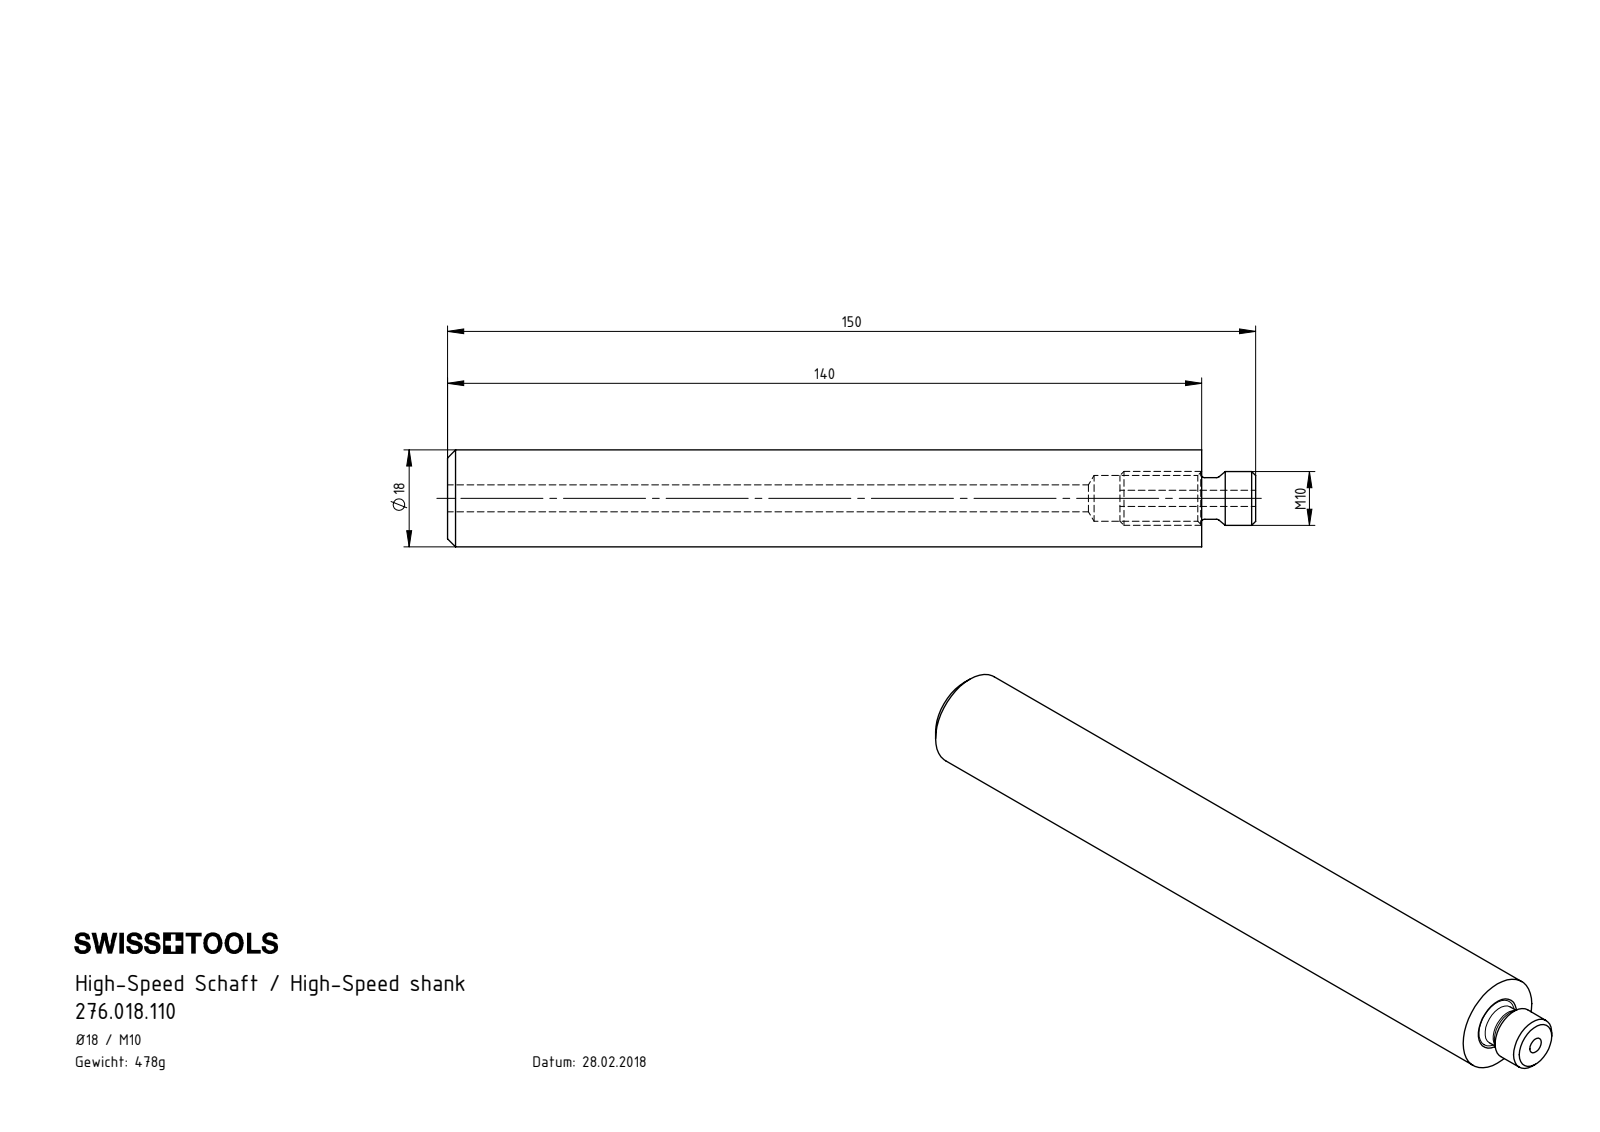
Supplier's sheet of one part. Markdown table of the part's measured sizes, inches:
| quantity | value |
| --- | --- |
| part name | 276.018.110; HM1-U18.001.140_A; HM1-BG1.010.025_A |
| STEP written by | SolidWorks 2017 (CONFIG_CONTROL_DESIGN) |
| units | inches |
| bodies | 2 solids, 35 faces (5 planar, 14 cylindrical, 16 other) |
| overall size | 5.906 × 0.709 × 0.709 |
| volume | 2.057 in³ |
| surface area | 18.42 in² |
| round holes (diameter × count) | 0.118 × 1, 0.197 × 1, 0.335 × 1 |
| round bosses / shafts (diameter × count) | 0.709 × 1, 0.394 × 1, 0.303 × 1 |
| main face-to-face distances | 5.512, 5.906, 0.394, 4.913, 0.598, 0.992, 5.504, 0.591, 0.402 |
